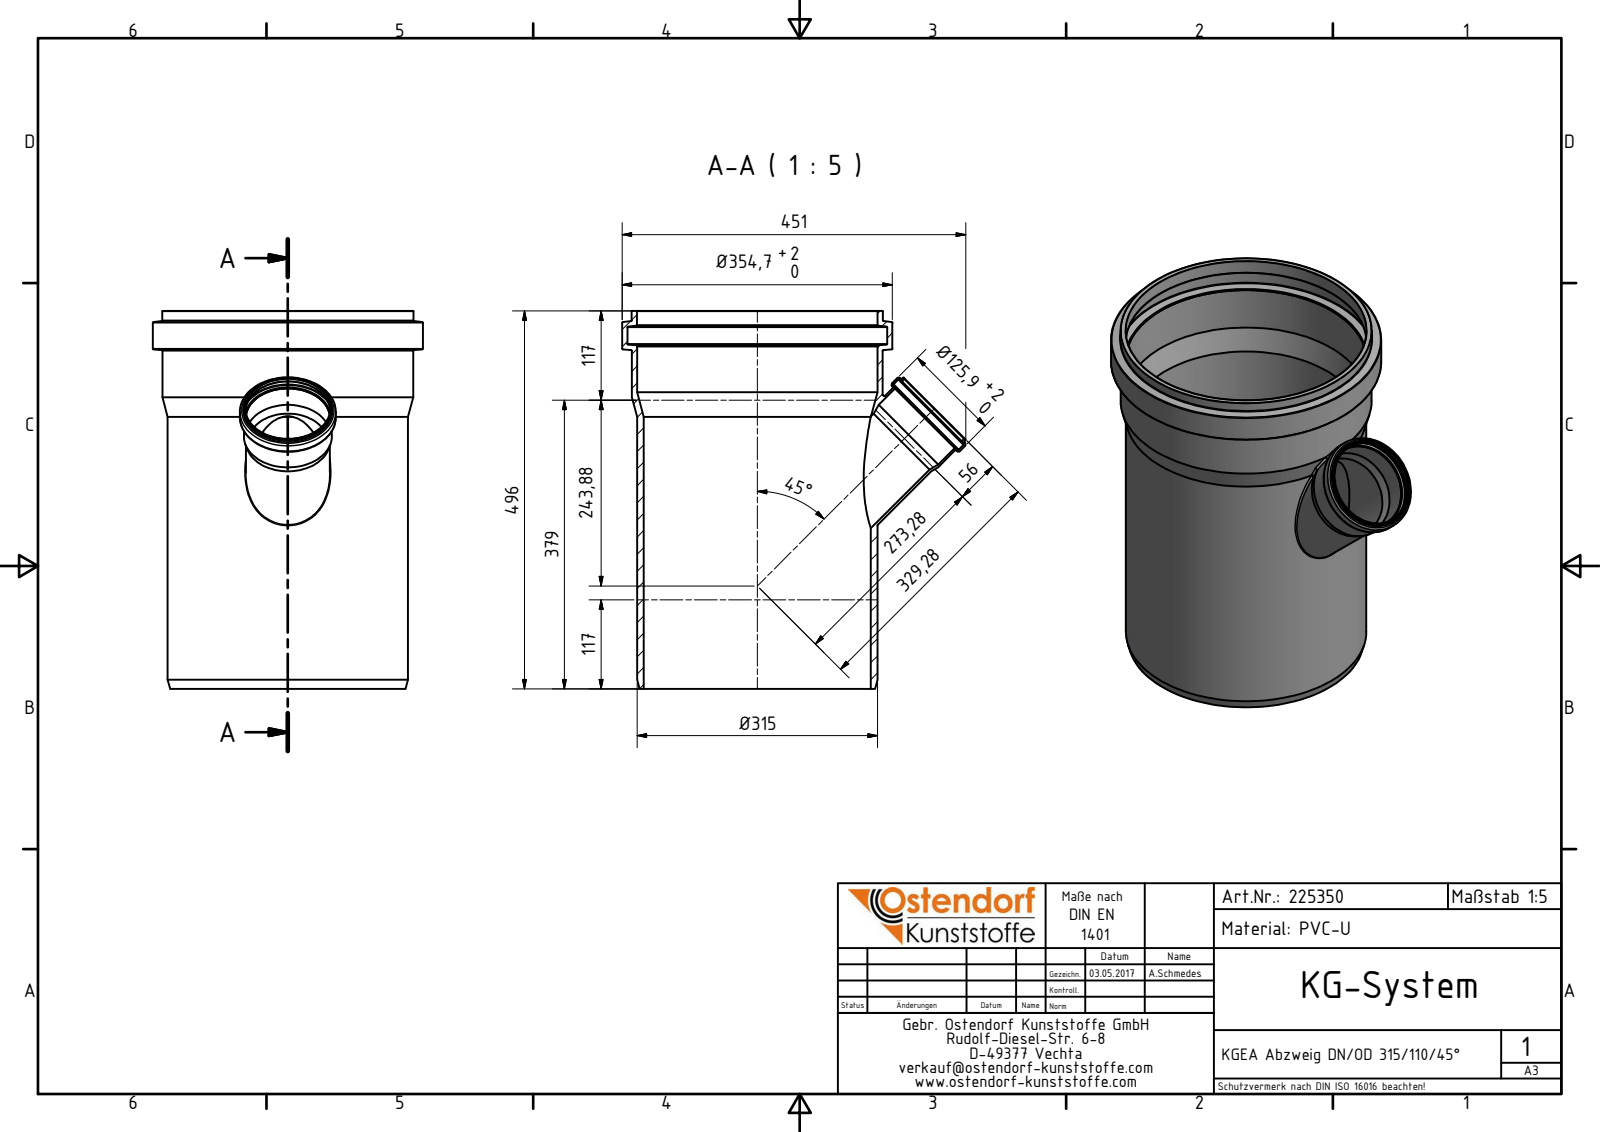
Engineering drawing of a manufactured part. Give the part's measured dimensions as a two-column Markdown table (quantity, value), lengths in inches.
| quantity | value |
| --- | --- |
| part name | 225350 KGEA Abzweig DN_OD 315_110_45° |
| STEP written by | Autodesk Inventor 2016 (AUTOMOTIVE_DESIGN) |
| units | inches |
| bodies | 1 solid, 64 faces (5 planar, 18 cylindrical, 41 other) |
| overall size | 19.528 × 17.756 × 13.965 |
| volume | 255.5 in³ |
| surface area | 1 696 in² |
| round holes (diameter × count) | 4.087 × 1, 4.358 × 1, 4.37 × 1, 4.768 × 1, 11.74 × 1, 12.425 × 1, 12.437 × 1, 13.421 × 1 |
| round bosses / shafts (diameter × count) | 13.965 × 1, 12.98 × 1, 12.969 × 1, 4.957 × 1, 4.559 × 1, 4.547 × 1, 4.339 × 1 |
| main face-to-face distances | 19.528, 17.694, 1.833, 0.717 |
